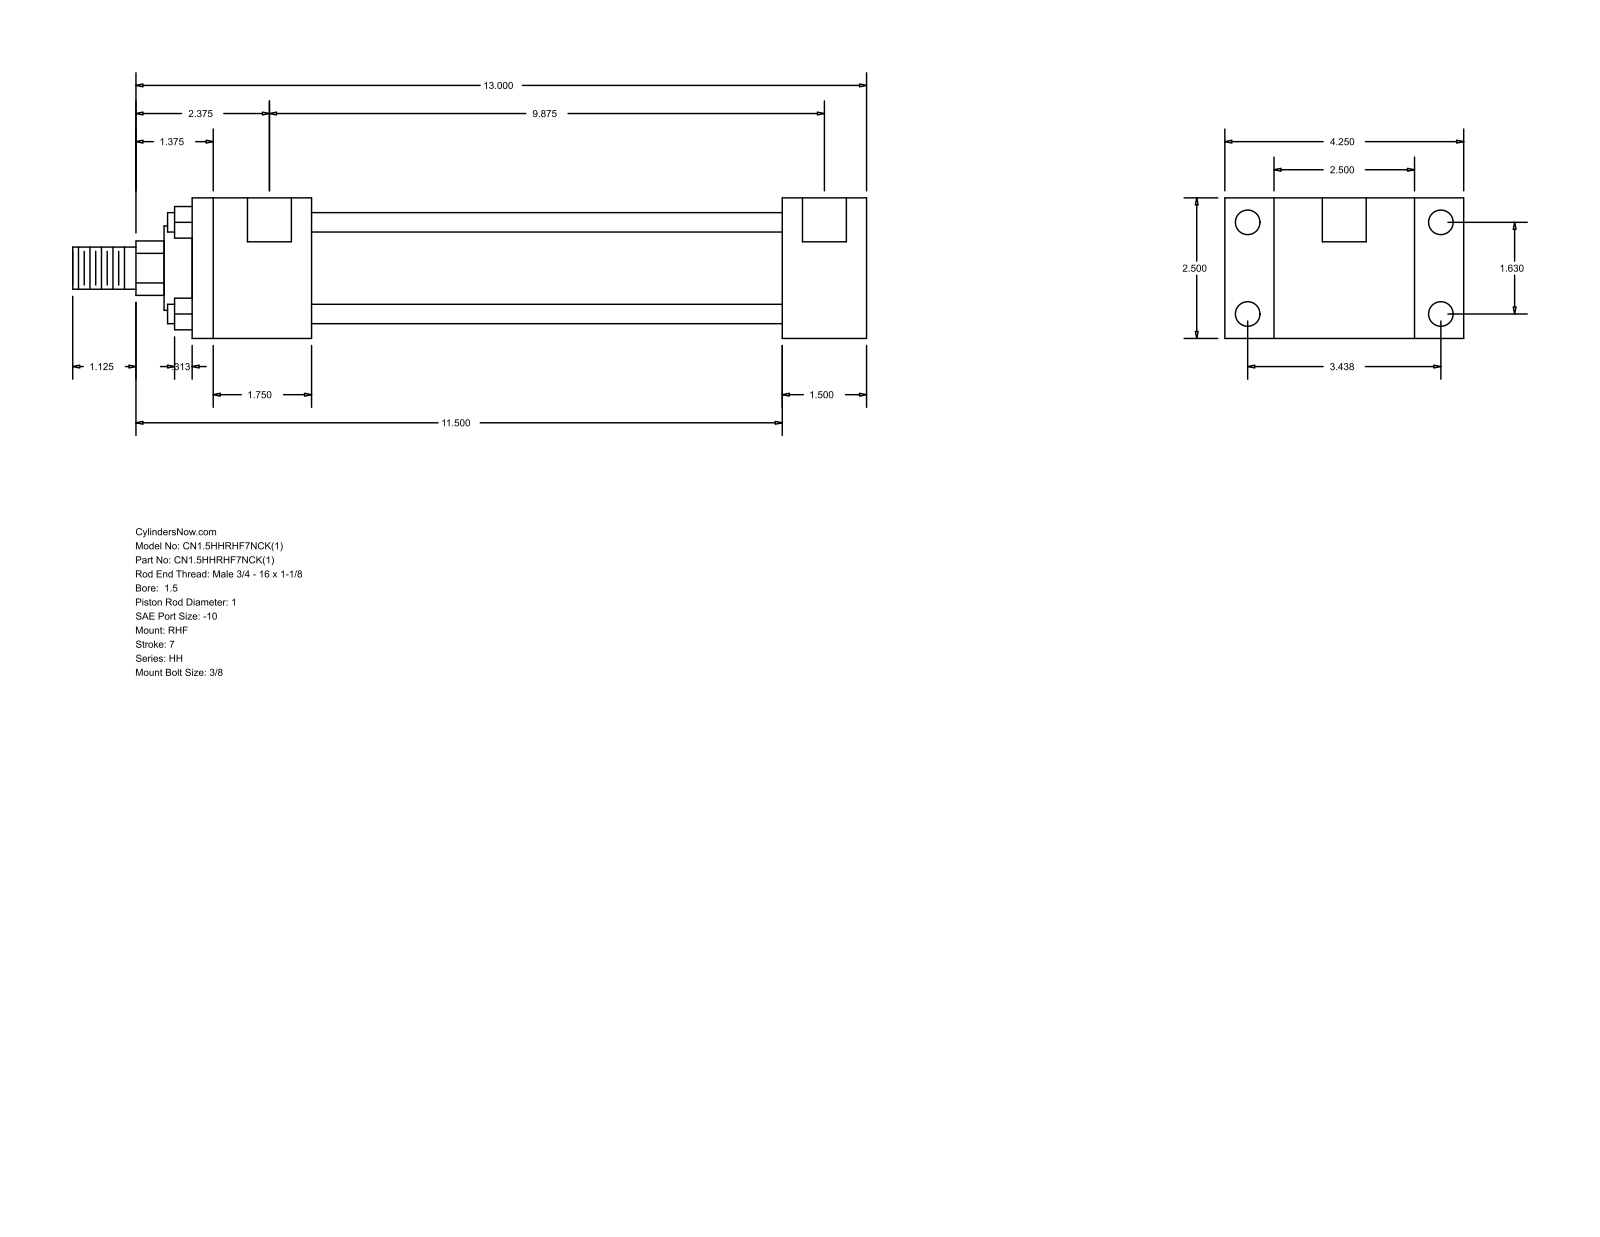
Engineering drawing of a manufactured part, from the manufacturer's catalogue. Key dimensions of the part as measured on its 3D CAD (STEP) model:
Part name (STEP PRODUCT): HH_RHF__0150_1
STEP written by: GSSL Pune (CONFIG_CONTROL_DESIGN)
Units: millimetres
Bodies: 0 solids, 88 faces (60 planar, 28 cylindrical, 0 other)
Overall size (bounding box): 358.77 × 107.95 × 63.5
Round holes (diameter × count): ⌀5.56 ×4, ⌀11.13 ×4, ⌀19.84 ×2
Round bosses / shafts (diameter × count): ⌀8.76 ×4, ⌀44.45 ×1, ⌀38.1 ×1, ⌀25.4 ×1, ⌀19.05 ×1
Partial cylindrical surfaces — rounded edges, fillets, slot ends (radius × count): R12.29 ×1
Main face-to-face distances: 63.5, 22.23, 85.73, 38.1, 107.96, 212.72, 250.82, 53.98, 266.7, 304.8
Hole centre spacings: 1.59, 41.4, 87.32, 96.64, 252.41, 254, 250.82
